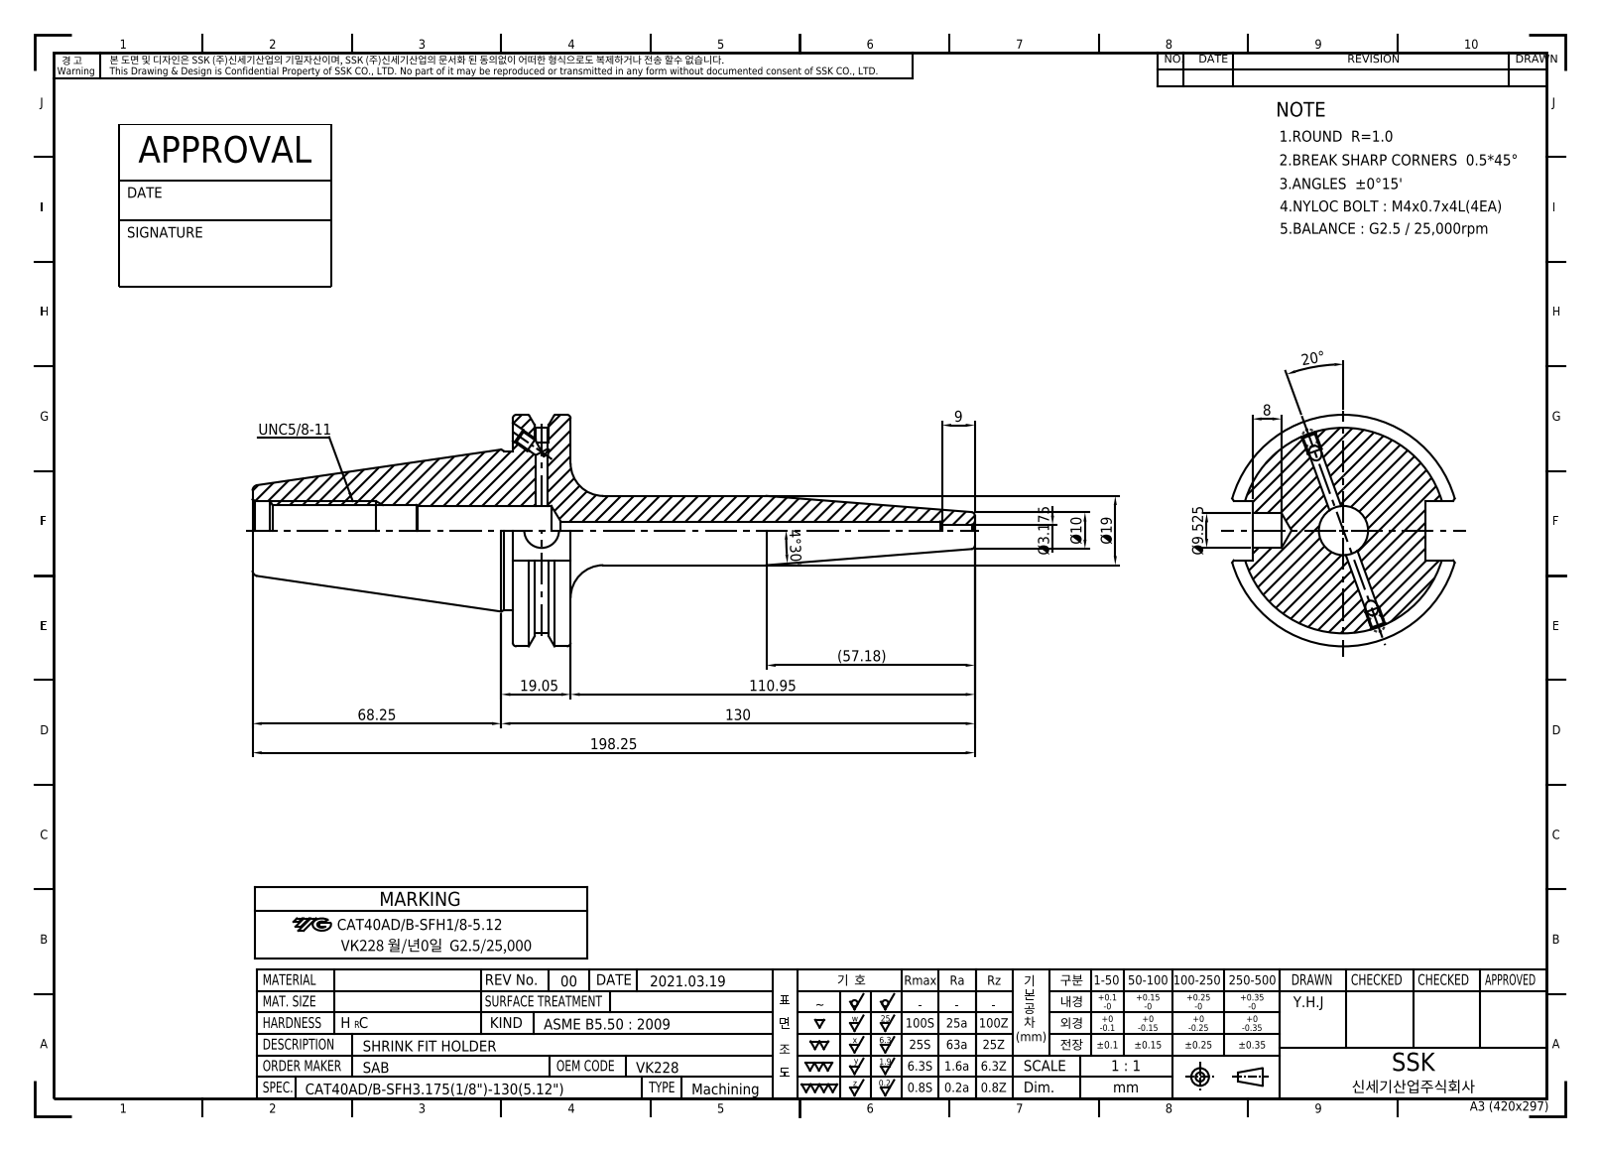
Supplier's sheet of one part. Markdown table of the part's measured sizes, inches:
| quantity | value |
| --- | --- |
| part name | LO-CAT40ADB-SFH3.175-130 |
| STEP written by | Autodesk Inventor 2022 (AUTOMOTIVE_DESIGN) |
| units | inches |
| bodies | 1 solid, 85 faces (35 planar, 28 cylindrical, 22 other) |
| overall size | 7.805 × 2.5 × 2.405 |
| volume | 7.655 in³ |
| surface area | 43.13 in² |
| round holes (diameter × count) | 0.128 × 4, 0.157 × 2, 0.165 × 2, 0.125 × 1, 0.197 × 1, 0.375 × 1, 0.512 × 1, 0.527 × 1, 0.642 × 1 |
| round bosses / shafts (diameter × count) | 2.5 × 1, 1.717 × 1, 0.748 × 1 |
| partial cylindrical surfaces (radius × count) | 1.108 × 1 |
| main face-to-face distances | 0.625, 1.874, 0.645, 2.812, 3.437, 3.05, 0.238, 0.387, 3.201, 0.389 |
